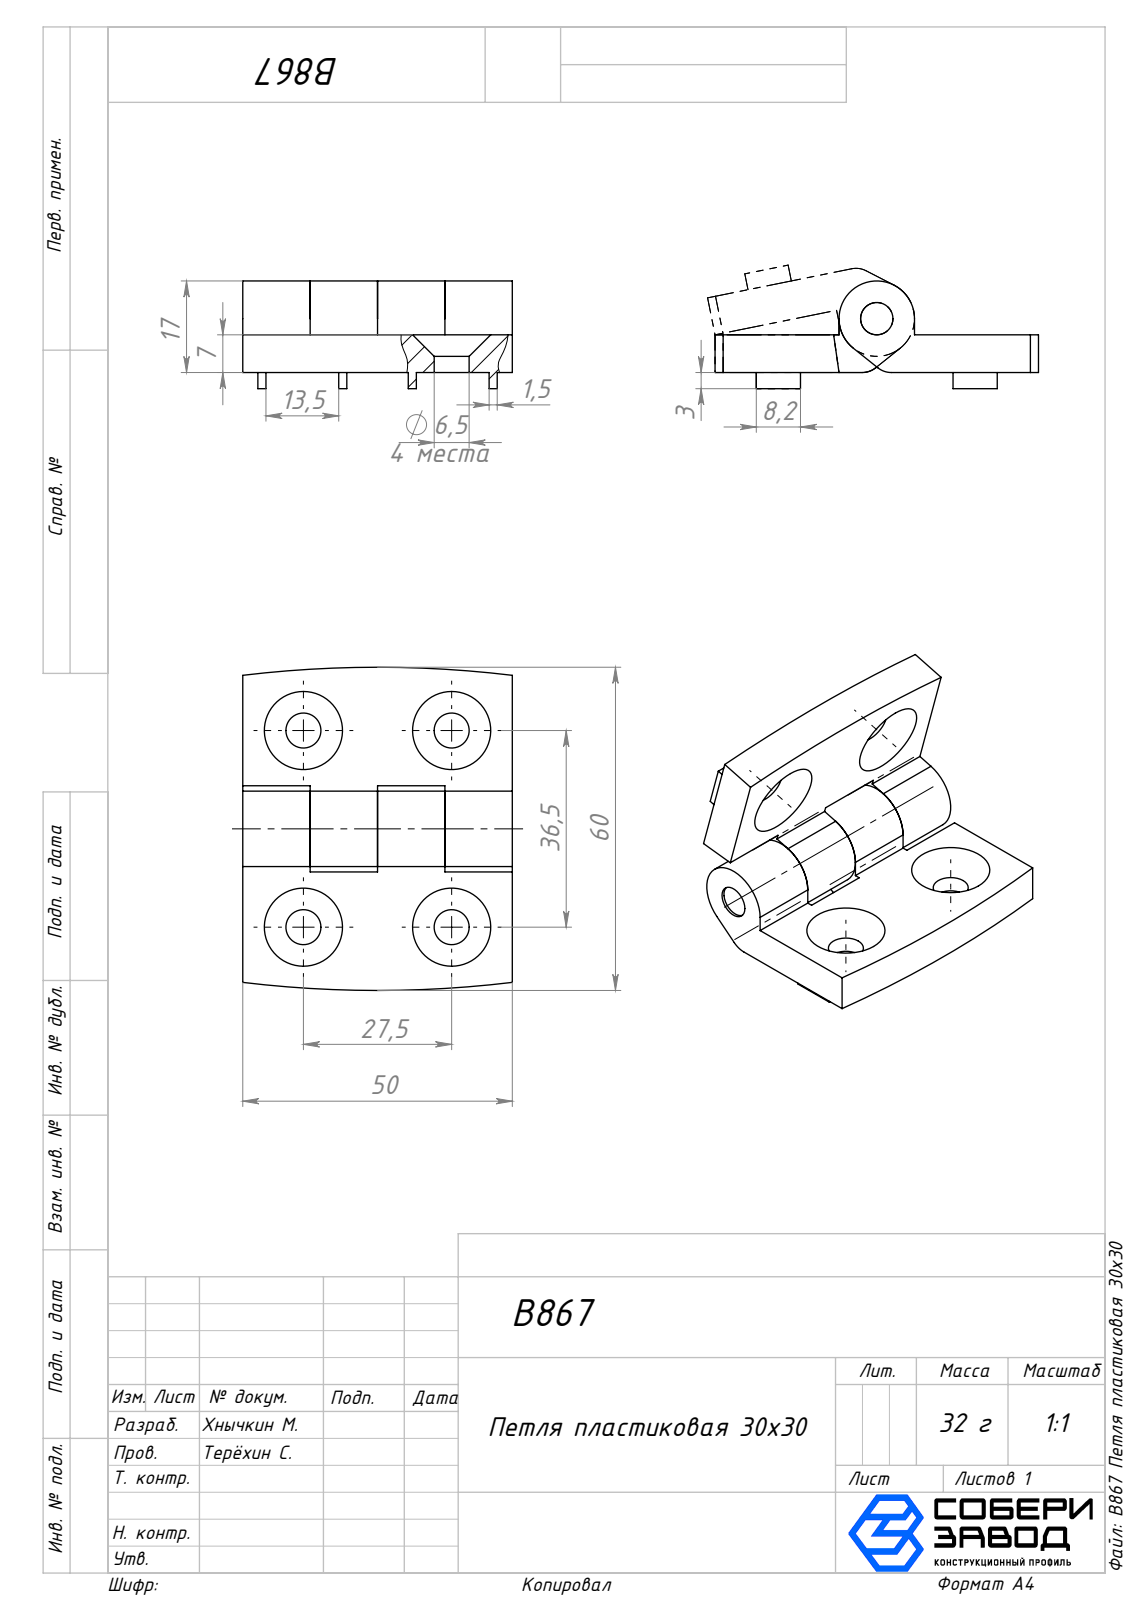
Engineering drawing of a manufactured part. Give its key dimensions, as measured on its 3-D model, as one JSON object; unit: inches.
{"part_name": "Петля 30_00; B867 Петля пластиковая 30х30; Палец_00", "step_written_by": "SolidWorks 2025 (AUTOMOTIVE_DESIGN)", "units": "inches", "bodies": {"solids": 3, "faces": 108, "planar": 68, "cylindrical": 32, "other": 8}, "overall_size": [1.969, 1.755, 1.539], "volume_in3": 1.424, "surface_area_in2": 18.81, "round_holes": [[0.256, 4], [0.236, 1]], "round_bosses_or_shafts": [[0.551, 1]], "partial_cylinders_radius": [[0.157, 2], [8.231, 2]], "face_to_face_distances": [0.276, 0.492, 0.984, 1.476, 1.969, 0.059, 0.591, 1.098, 0.323, 0.11], "hole_center_spacings": [1.083]}
